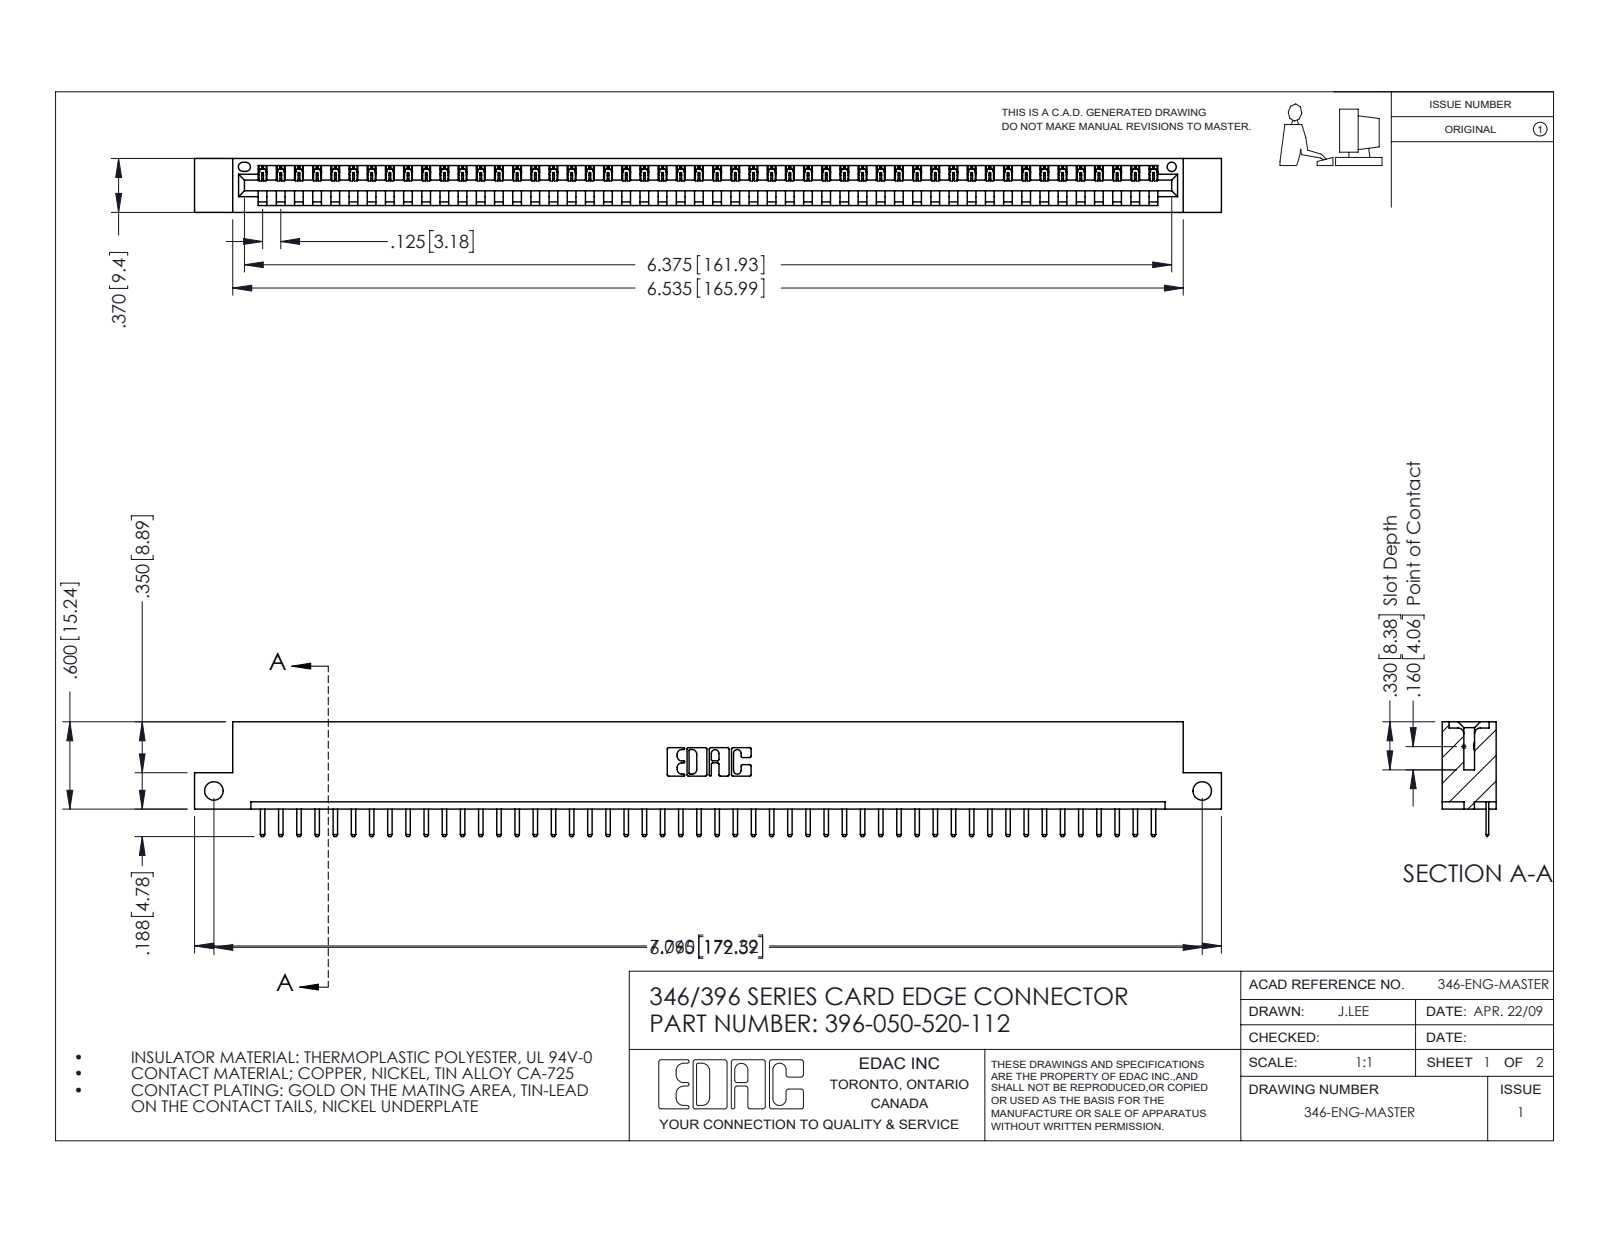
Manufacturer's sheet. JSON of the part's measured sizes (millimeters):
{"part_name": "396-050-520-112; 345-292-001_345-293-120; 346 Part_Flush Mounting Lugs - Side Mount", "step_written_by": "SolidWorks 2016 (CONFIG_CONTROL_DESIGN)", "units": "millimeters", "bodies": {"solids": 51, "faces": 3222, "planar": 2176, "cylindrical": 1046, "other": 0}, "overall_size": [179.3, 20, 9.4], "volume_mm3": 16990, "surface_area_mm2": 20700, "round_holes": [[3.3, 2], [1.6, 1]], "partial_cylinders_radius": [[0.3, 102], [0.2, 100], [0.3, 22], [0.2, 6], [0.8, 6], [0.7, 3], [0.8, 2], [1, 2]], "face_to_face_distances": [1.2, 8.2, 9.4, 6.4, 3.8, 5.6, 2.5, 4.4, 1.8, 7.6], "hole_center_spacings": [172.6]}
